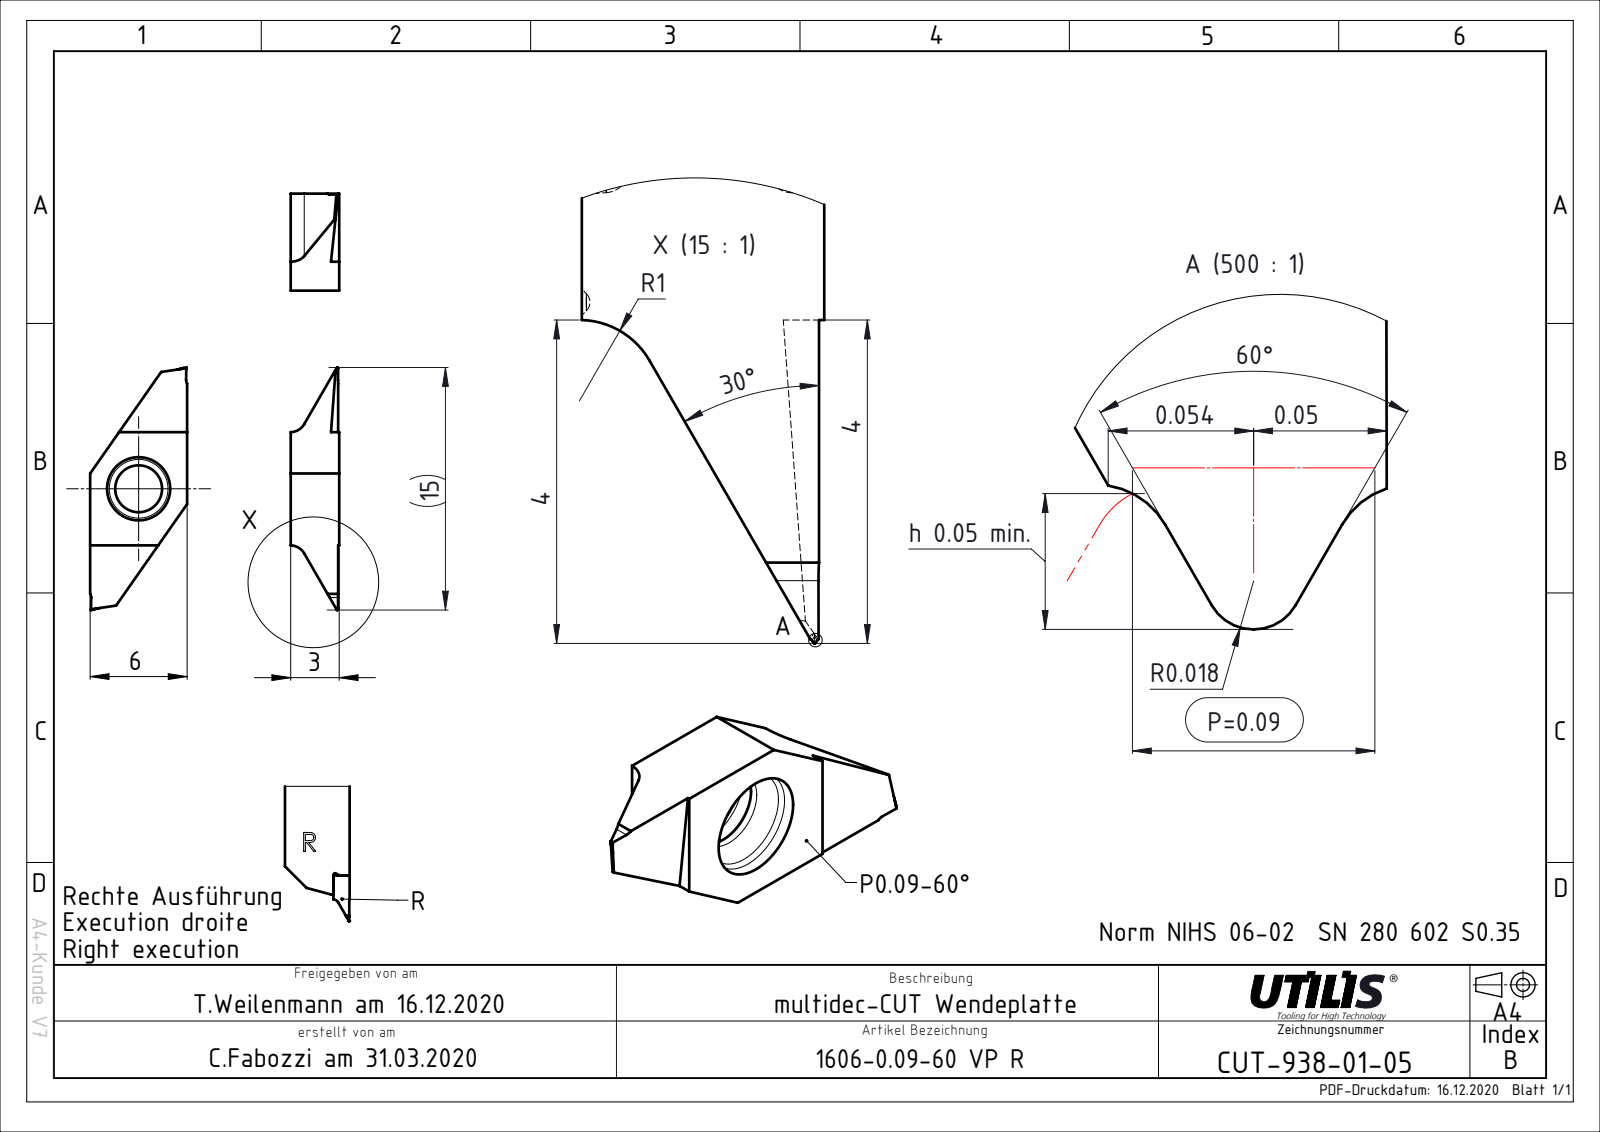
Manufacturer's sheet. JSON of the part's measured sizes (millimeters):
{"part_name": "CUT-938-01; ASME Y14.5", "step_written_by": "FormatWorks Professional (AP242_MANAGED_MODEL_BASED_3D_ENGINEERING_MIM_LF)", "units": "millimeters", "bodies": {"solids": 1, "faces": 36, "planar": 22, "cylindrical": 14, "other": 0}, "overall_size": [52.95, 16.56, 3.31], "volume_mm3": 124, "surface_area_mm2": 307, "round_holes": [[2.9, 1]], "partial_cylinders_radius": [[1, 2]], "face_to_face_distances": [6, 3, 9, 7, 12, 7.19, 7.2]}
